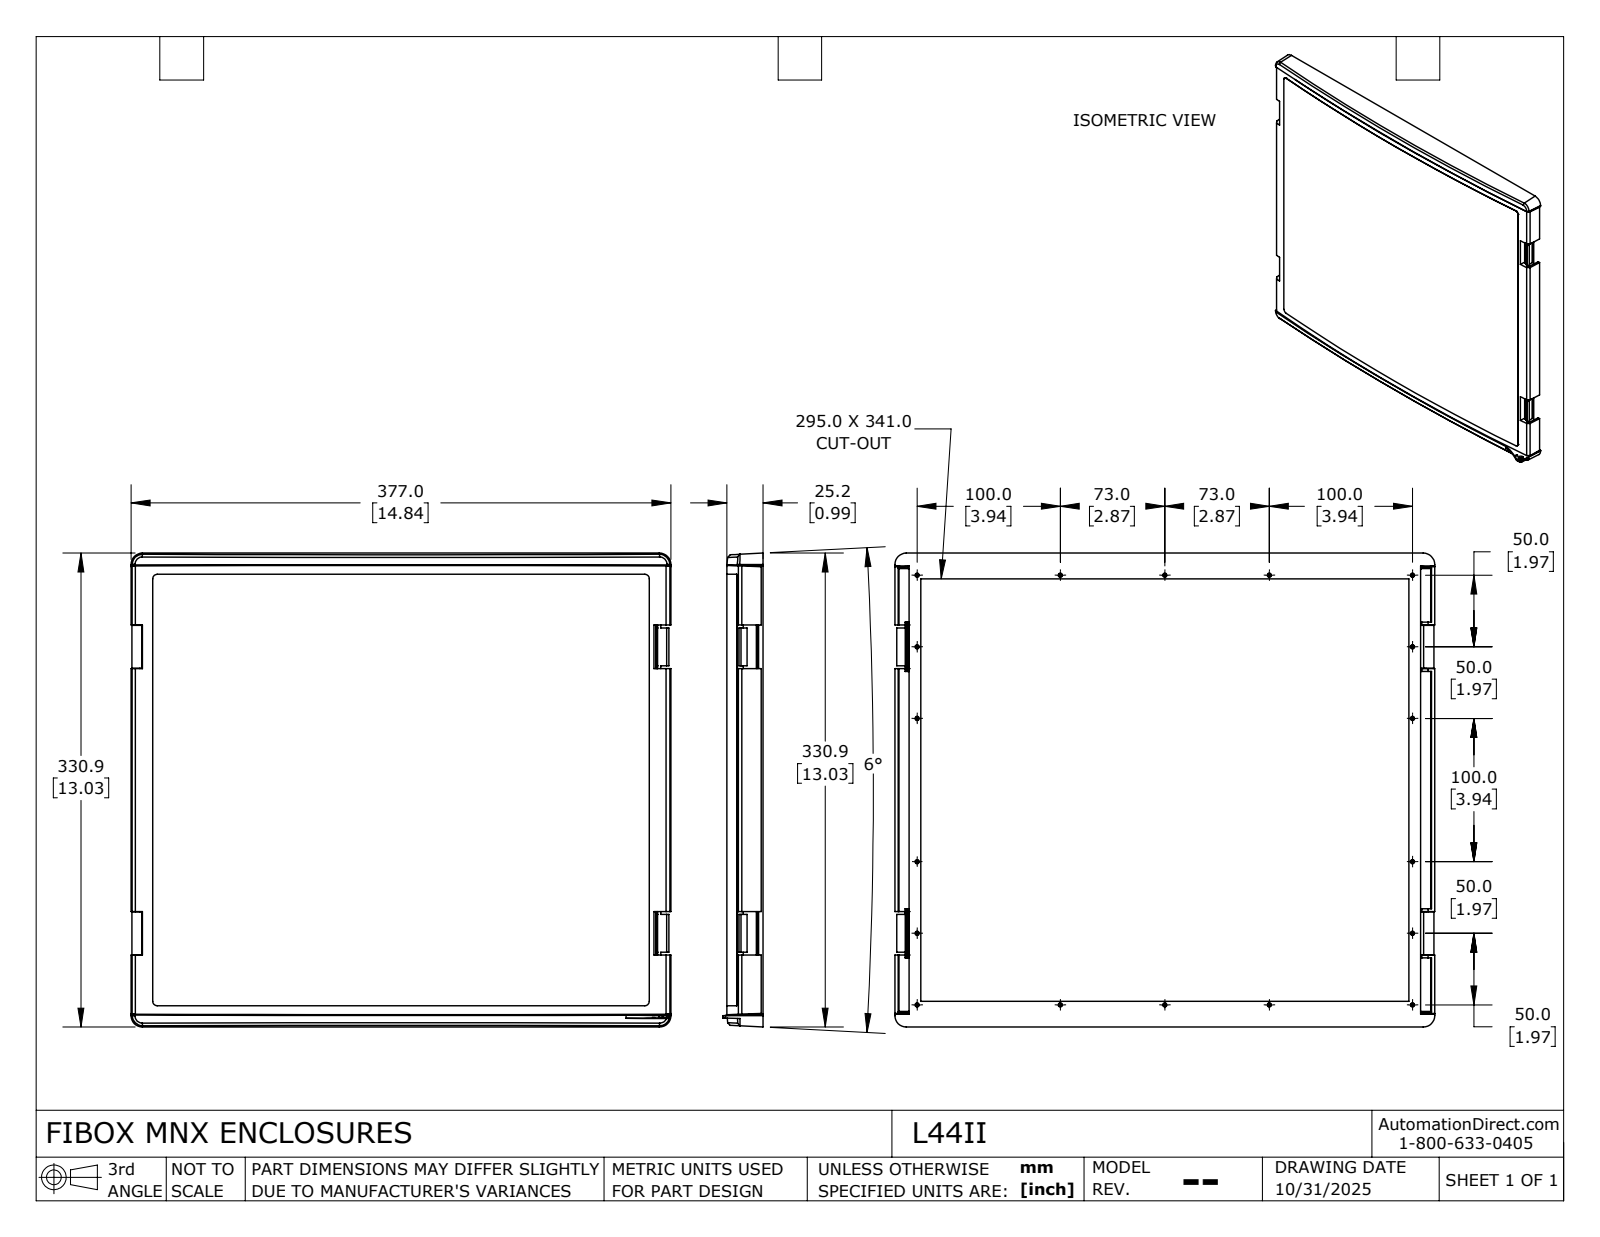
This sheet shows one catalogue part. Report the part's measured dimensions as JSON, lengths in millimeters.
{"part_name": "L44II_Default", "step_written_by": "SolidWorks 2024 (CONFIG_CONTROL_DESIGN)", "units": "millimeters", "bodies": {"solids": 2, "faces": 305, "planar": 179, "cylindrical": 96, "other": 30}, "overall_size": [377.1, 330.9, 28.1], "volume_mm3": 634300, "surface_area_mm2": 358800, "round_holes": [[2.2, 18], [2.9, 18]], "round_bosses_or_shafts": [[5, 1]], "partial_cylinders_radius": [[4.5, 3], [1, 1], [2.6, 1], [2137.5, 1], [2140, 1], [2140, 1]], "face_to_face_distances": [13, 12.9, 0.6, 9.9, 2.2, 7.7, 307.3, 306.7, 295, 341], "hole_center_spacings": [100, 50, 349.6, 200, 346, 360.2, 399.6, 300]}
